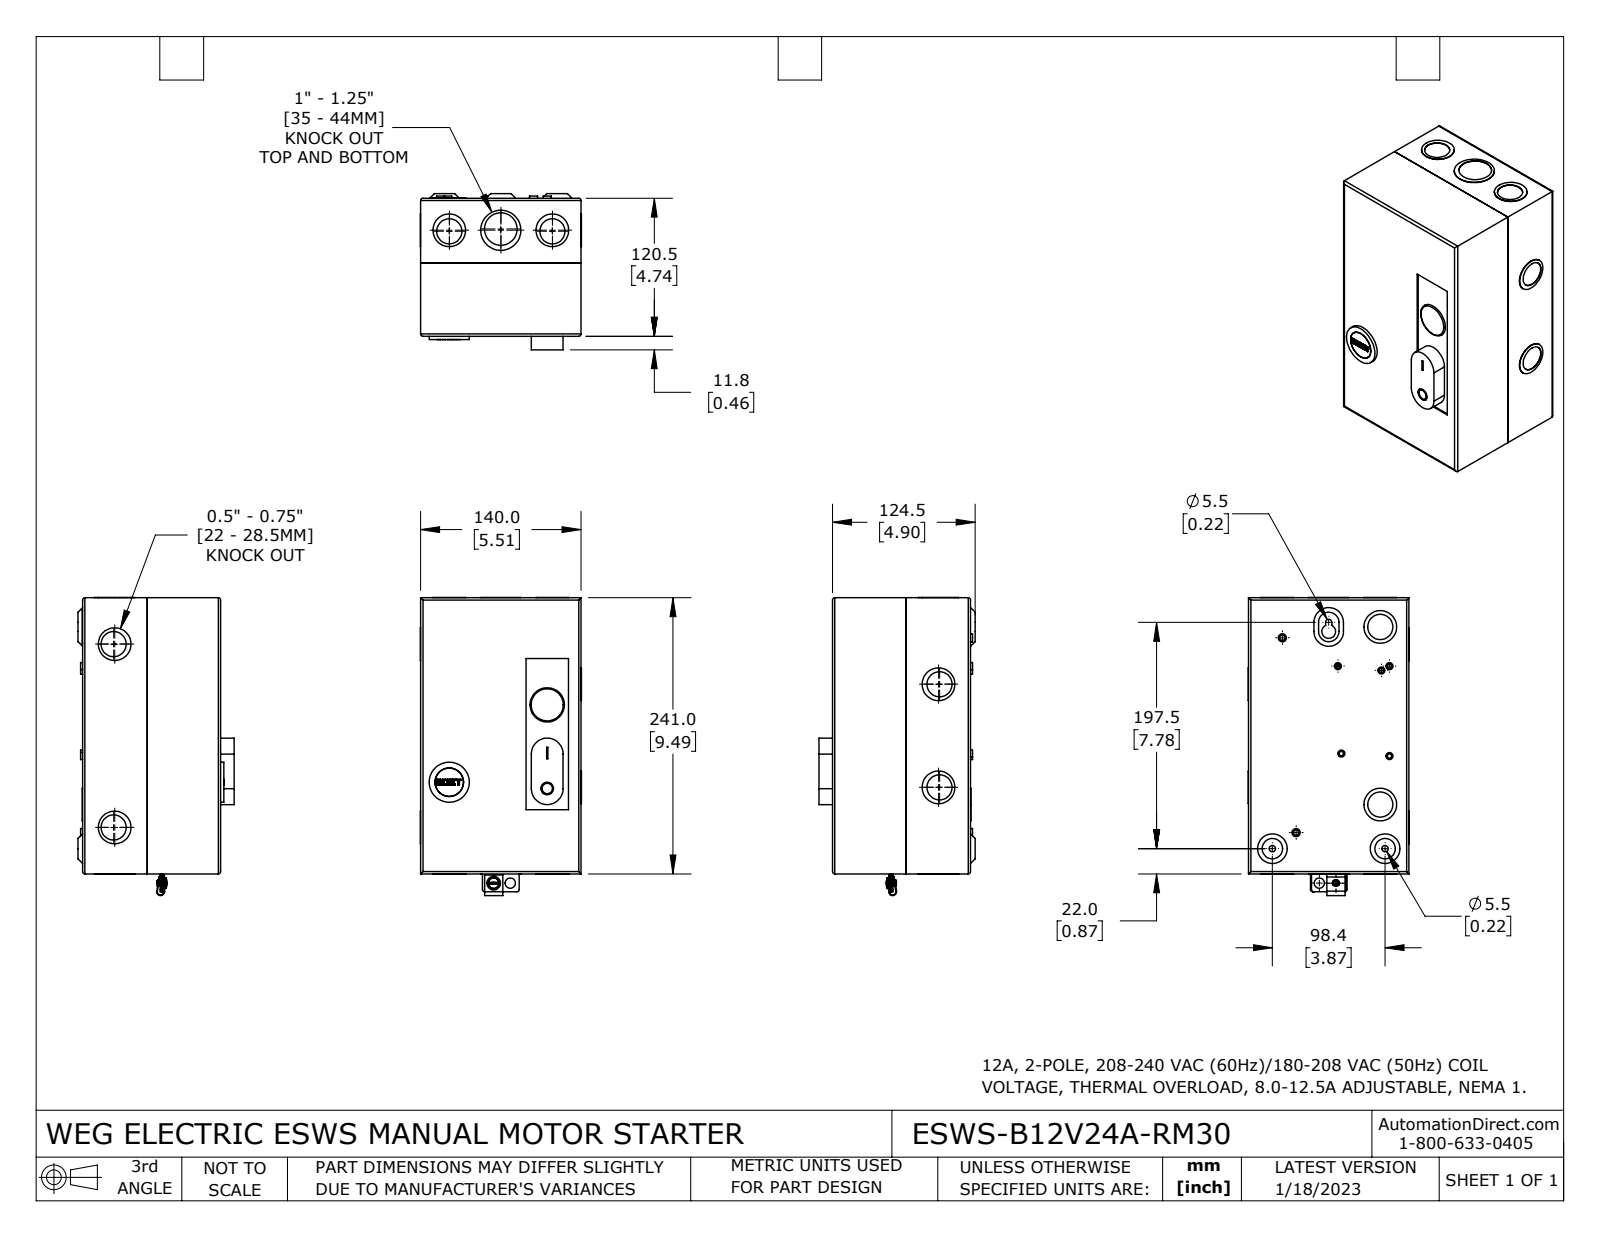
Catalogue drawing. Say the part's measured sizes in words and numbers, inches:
The part is named "ESWS-B12V24A-RM30". Its 3-D file was written by "SolidWorks 2021 (CONFIG_CONTROL_DESIGN)". It is 7 solids with 435 faces: 168 planar, 230 cylindrical and 37 other. Overall it measures 10.248 by 5.535 by 5.366 inches. Its volume is 16.23 cubic inches and its surface area 585.2 square inches. Round holes: 5 of diameter 0.146, 4 of diameter 0.864, 2 of diameter 0.183, 2 of diameter 0.217, 2 of diameter 0.354, 2 of diameter 0.864, 2 of diameter 0.866, 2 of diameter 0.886, 1 of diameter 0.256, 1 of diameter 0.303, 1 of diameter 0.433, 1 of diameter 0.469. Round bosses or shafts: 6 of diameter 1.124, 5 of diameter 0.24, 2 of diameter 1.122, 2 of diameter 0.278, 1 of diameter 1.38, 1 of diameter 1.378, 1 of diameter 1.193, 1 of diameter 1.148. Partial cylindrical surfaces (rounded edges, fillets, slot ends): 34 of radius 0.004, 13 of radius 0.079, 4 of radius 0.031, 3 of radius 0.108, 2 of radius 0.059, 2 of radius 0.075, 2 of radius 0.122, 2 of radius 0.138. The main face-to-face distances are 0.047, 4.697, 5.465, 4.65, 9.441, 4.744, 5.417, 5.512, 0.071, 0.063. The hole center spacings are 0.571, 1.378, 1.773, 3.387, 3.543, 4.921, 5.995, 7.484.
